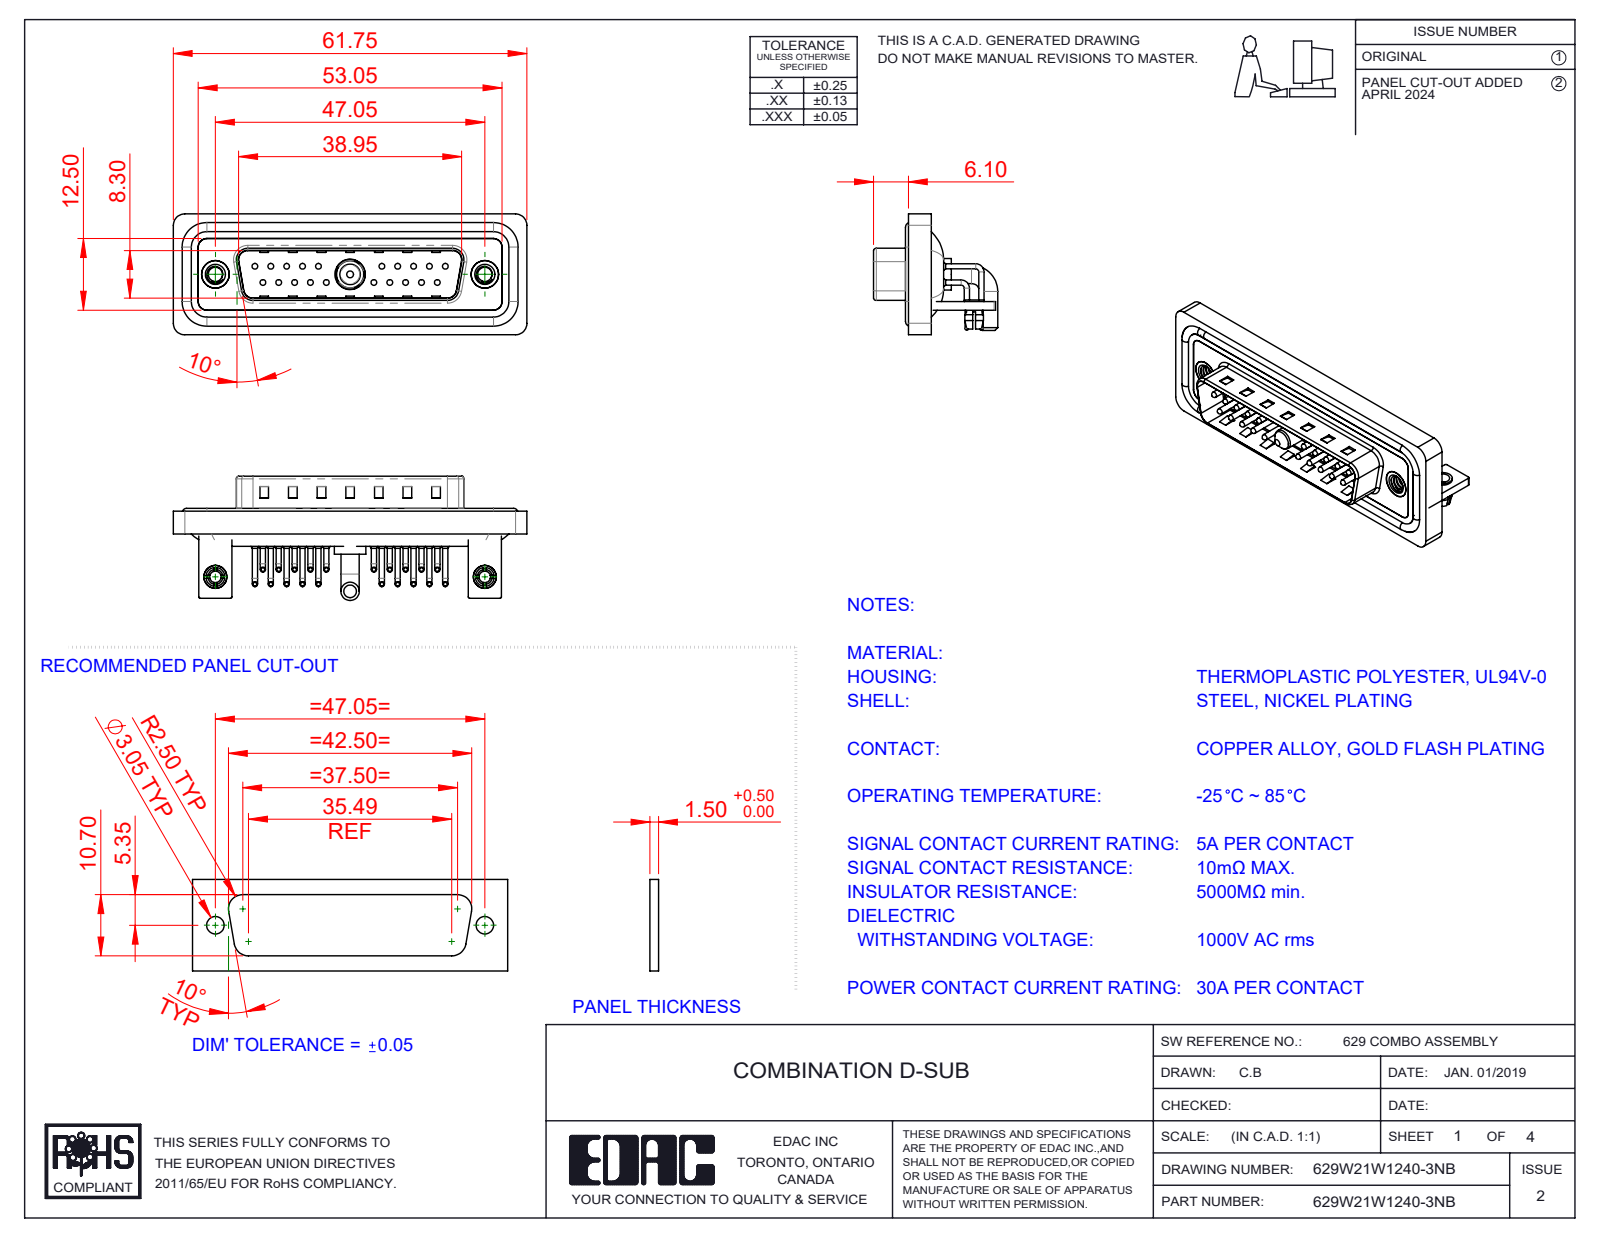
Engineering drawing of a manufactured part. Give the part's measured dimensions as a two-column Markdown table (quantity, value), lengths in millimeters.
| quantity | value |
| --- | --- |
| part name | 629Combo Contact Row 1; 629Combo Waterproof Housing_25 Contacts; 629Combo Shell Front_25 Contacts; 629Combo Housing_21W1 (+7 more) |
| STEP written by | SolidWorks 2023 (CONFIG_CONTROL_DESIGN) |
| units | millimeters |
| bodies | 33 solids, 2856 faces (1567 planar, 979 cylindrical, 310 other) |
| overall size | 61.75 × 21.7 × 21.1 |
| volume | 7 754 mm³ |
| surface area | 13 538 mm² |
| round holes (diameter × count) | 2 × 22, 0.75 × 20, 1.6 × 20, 2.5 × 4, 3.2 × 2, 4 × 2, 4.8 × 2, 5 × 2, 4.85 × 1, 5.3 × 1 |
| round bosses / shafts (diameter × count) | 0.9 × 40, 1.5 × 20, 1 × 20, 0.65 × 20, 1.6 × 4, 4.9 × 2, 4 × 2, 3.4 × 2 |
| partial cylindrical surfaces (radius × count) | 1.01 × 20, 2 × 19, 1.5 × 18, 0.25 × 16, 0.5 × 9, 1.6 × 8, 0.6 × 4, 0.65 × 4 |
| main face-to-face distances | 0.4, 0.8, 2.1, 2.9, 1.5, 1.1, 4.1, 1.6, 4.5, 3.7 |
| hole center spacings | 3.16, 2.77, 5.54, 8.31, 5.04, 19.39, 20.97, 22.16 |
